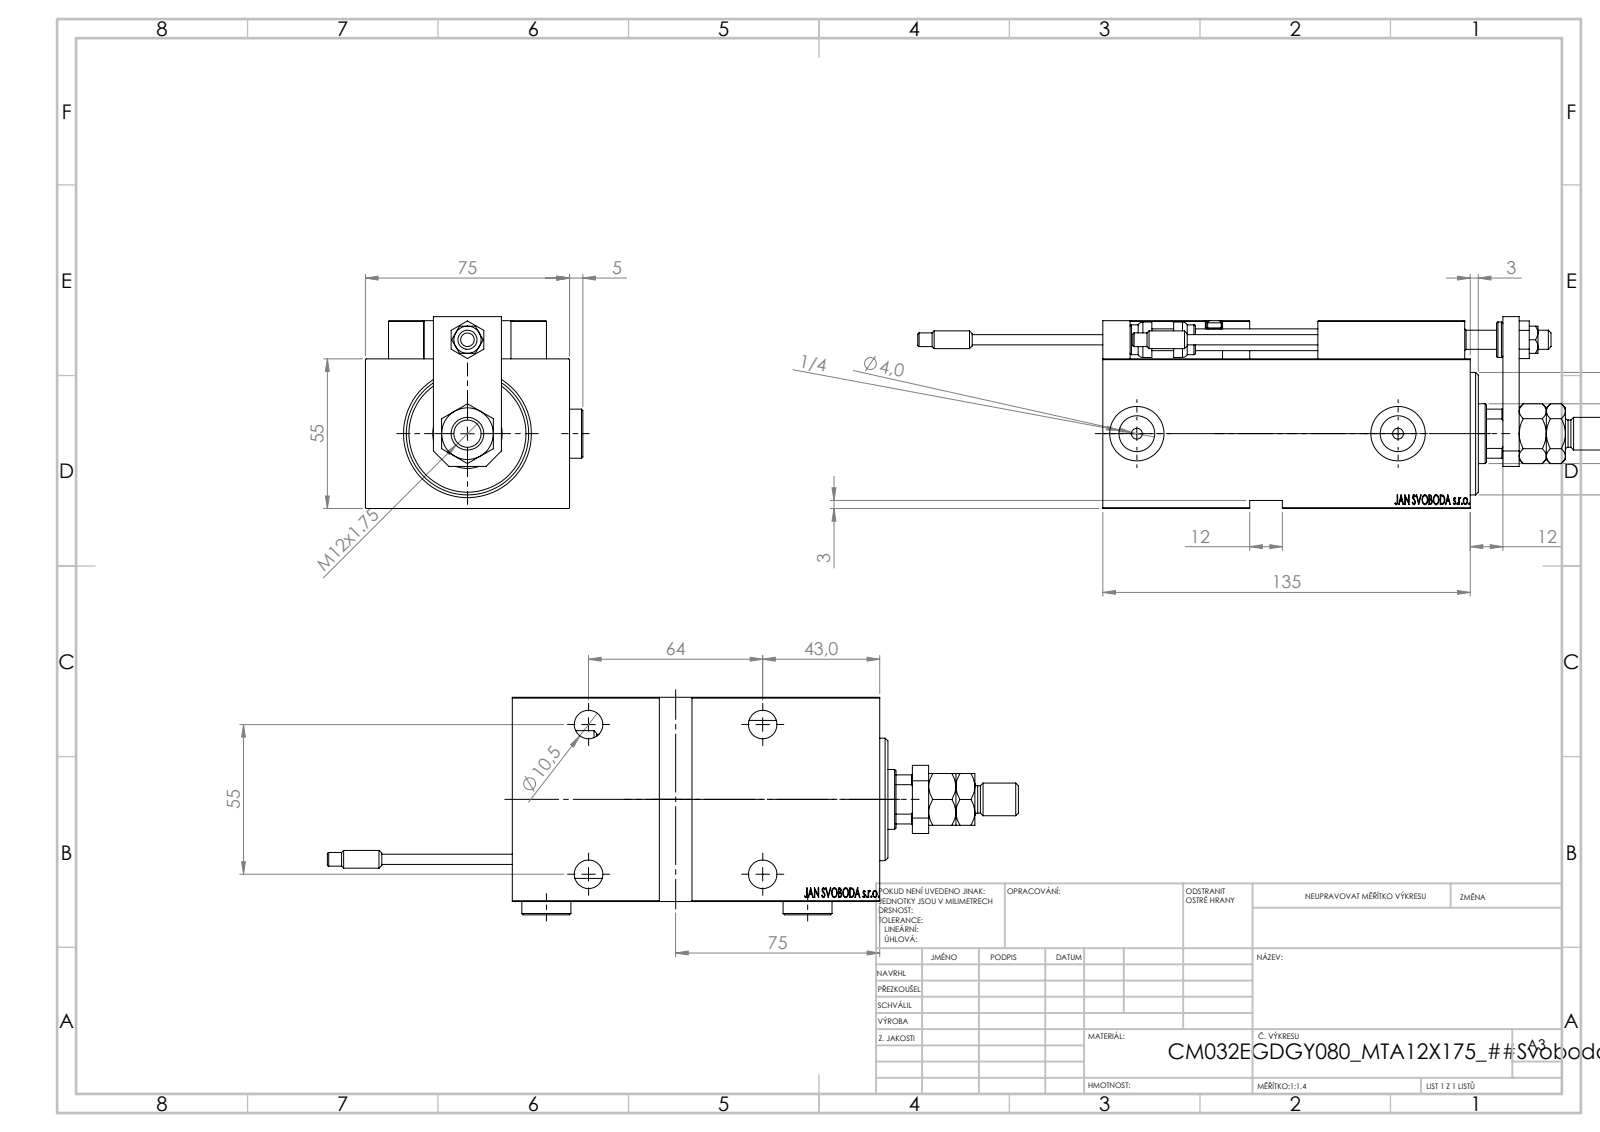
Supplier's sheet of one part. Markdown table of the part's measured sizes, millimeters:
| quantity | value |
| --- | --- |
| part name | V450CM_E_Body; ZARAZKA; TYC_L79; SWITCH_X_FRONT_BACK (+7 more) |
| STEP written by | SolidWorks 2019 (CONFIG_CONTROL_DESIGN) |
| units | millimeters |
| bodies | 27 solids, 1417 faces (622 planar, 208 cylindrical, 587 other) |
| overall size | 254 × 79.9 × 70.5 |
| volume | 555 517 mm³ |
| surface area | 116 174 mm² |
| round holes (diameter × count) | 4 × 6, 8 × 5, 10.5 × 5, 16.5 × 5, 3.2 × 4, 5 × 2, 13.16 × 2, 20 × 2, 7 × 1, 22 × 1, 25.5 × 1, 32 × 1 |
| round bosses / shafts (diameter × count) | 5 × 4, 18 × 2, 6.5 × 2, 3.8 × 2, 34 × 1, 13 × 1, 12 × 1, 11 × 1 |
| partial cylindrical surfaces (radius × count) | 0.3 × 30, 3 × 2, 10.5 × 1 |
| main face-to-face distances | 55, 75, 3, 69, 10, 14, 12, 135, 5, 25 |
| hole center spacings | 11.37, 20, 28.9, 29.59, 29.69, 36.06, 40.03, 42.19 |
